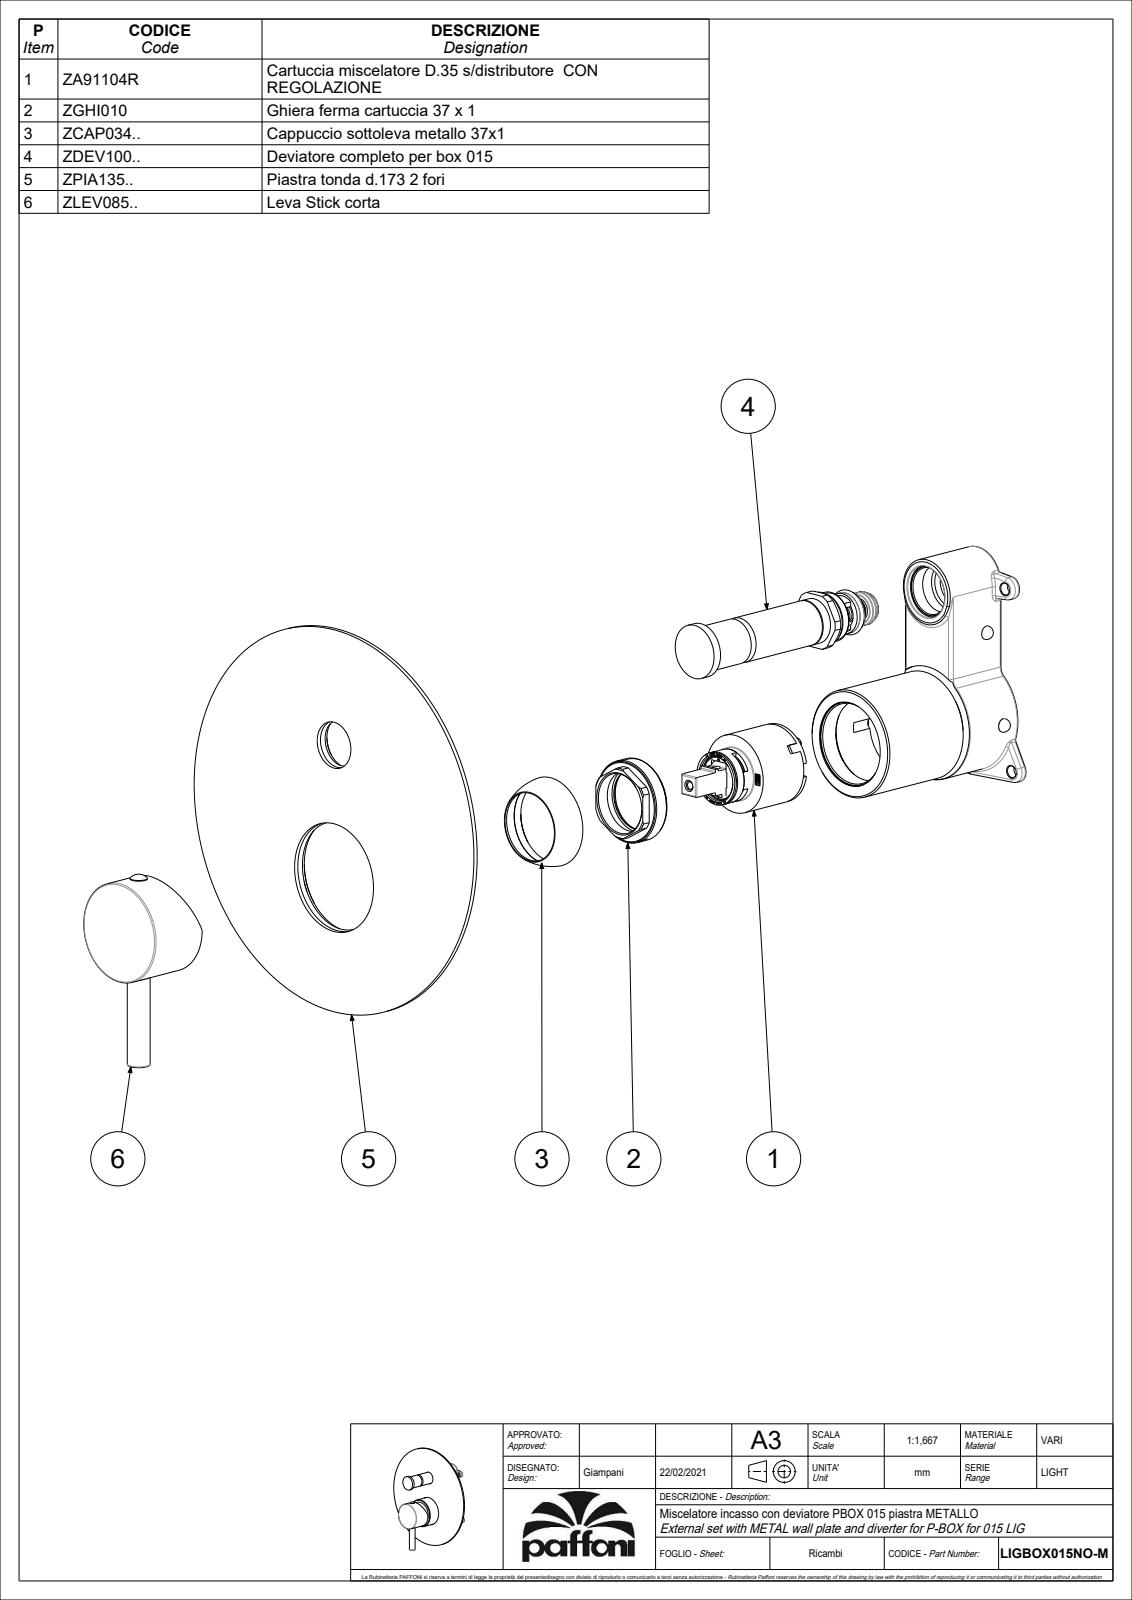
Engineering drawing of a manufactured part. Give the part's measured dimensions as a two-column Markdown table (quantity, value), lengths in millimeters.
| quantity | value |
| --- | --- |
| part name | LIGBOX015NO-M |
| STEP written by | CREO PARAMETRIC BY PTC INC, 2020044 (CONFIG_CONTROL_DESIGN) |
| units | millimeters |
| bodies | 4 solids, 971 faces (570 planar, 216 cylindrical, 185 other) |
| overall size | 174.25 × 173 × 55.19 |
| volume | 106 428 mm³ |
| surface area | 86 205 mm² |
| round holes (diameter × count) | 4 × 2, 3 × 1, 3.3 × 1, 5 × 1, 7.1 × 1, 16 × 1, 18.2 × 1, 19.5 × 1, 19.9 × 1, 20.8 × 1, 26.8 × 1, 29 × 1 |
| round bosses / shafts (diameter × count) | 173 × 1, 48.1 × 1, 44.5 × 1, 35 × 1, 24 × 1, 23.5 × 1, 23.4 × 1, 21.8 × 1 |
| partial cylindrical surfaces (radius × count) | 0.5 × 14, 0.15 × 11, 0.3 × 4, 1 × 2, 2.5 × 1, 6.5 × 1, 7 × 1, 9.3 × 1 |
| main face-to-face distances | 2, 50.8, 48.8, 9, 5.5, 23, 15.5, 17.5, 33.3, 27.8 |
| hole center spacings | 11.7, 60 |
